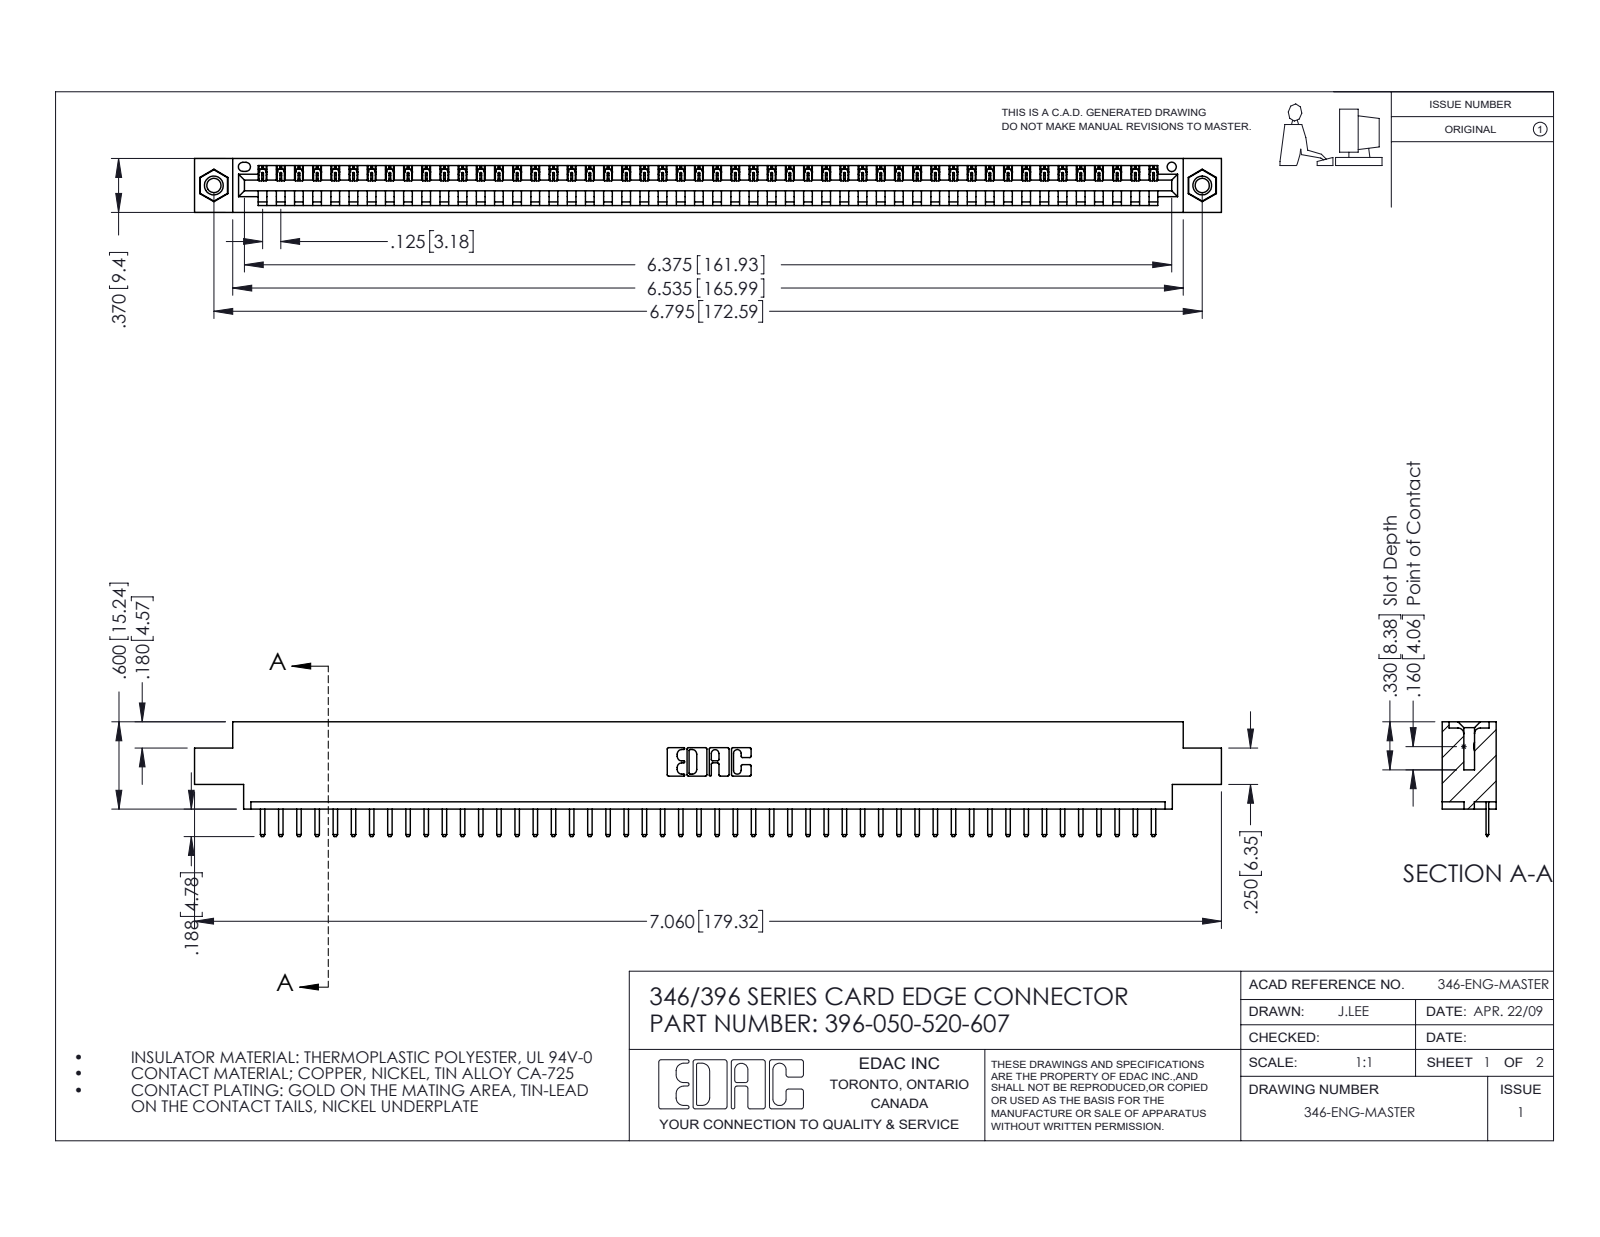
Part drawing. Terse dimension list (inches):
name: 346 Part_0.170 Offset - 0.156 Dia-TI; 345-250-001_345-250-005-103; 396-050-520-607; 345-292-001_345-293-120
written by: SolidWorks 2016 (CONFIG_CONTROL_DESIGN)
unit: in
bodies: 53 solids, 3286 faces (2212 planar, 1058 cylindrical, 16 other)
size: 7.06 × 0.788 × 0.37
volume: 1.032 in³; area: 32.45 in²
holes: 2× ⌀0.098, 2× ⌀0.125, 2× ⌀0.156, 1× ⌀0.064
bosses: 2× ⌀0.155
rounds: 102× R0.01, 100× R0.006, 22× R0.01, 6× R0.007, 6× R0.031, 3× R0.026, 2× R0.031, 2× R0.04
face distances: 0.048, 0.322, 0.37, 0.25, 0.222, 0.148, 0.1, 0.174, 0.072, 0.298
hole spacings: 0.246, 6.586, 6.795
